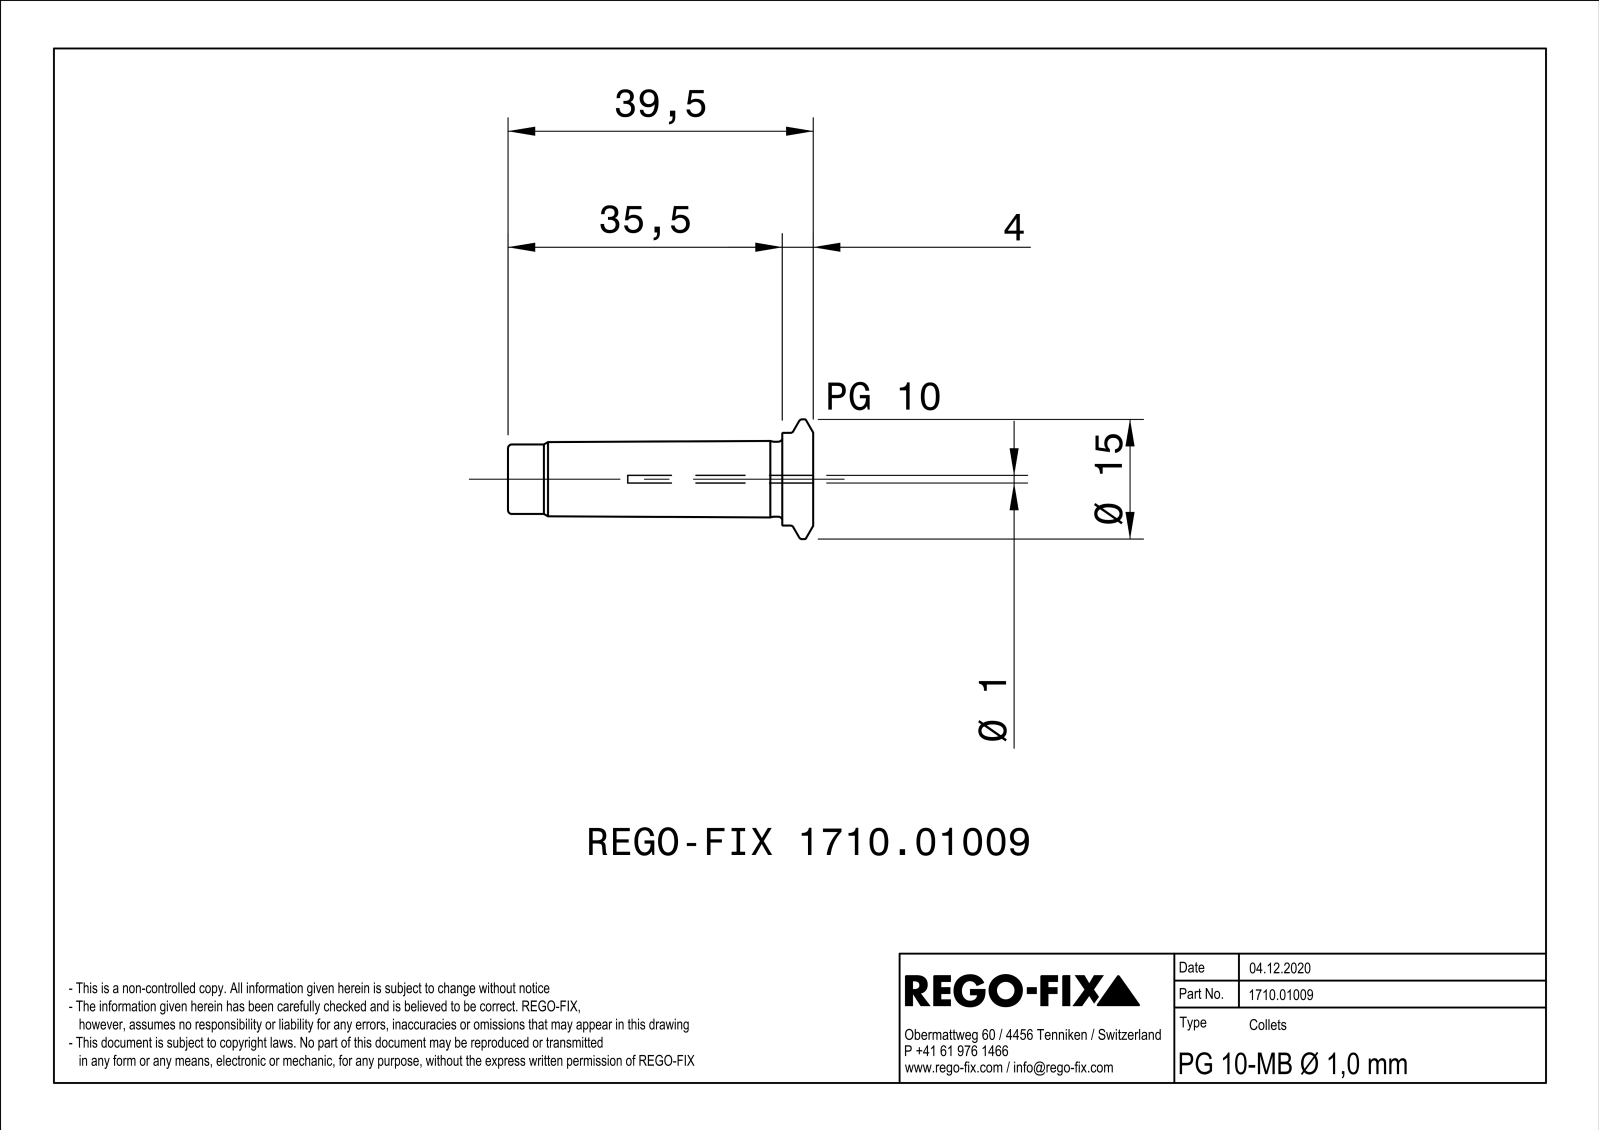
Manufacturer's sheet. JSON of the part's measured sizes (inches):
{"part_name": "NOCUT", "step_written_by": "SIEMENS PLM Software Solid Edge ST10 (AUTOMOTIVE_DESIGN)", "units": "inches", "bodies": {"solids": 1, "faces": 79, "planar": 21, "cylindrical": 18, "other": 40}, "overall_size": [1.555, 0.61, 0.61], "volume_in3": 0.138, "surface_area_in2": 4.18, "round_holes": [[0.079, 3], [0.039, 1], [0.244, 1], [0.268, 1]], "round_bosses_or_shafts": [[0.61, 1], [0.472, 1], [0.382, 1], [0.354, 1]], "face_to_face_distances": [0.024, 1.555, 0.768, 0.787, 1.398, 0.63, 0.157], "hole_center_spacings": [0.079, 0.136]}
